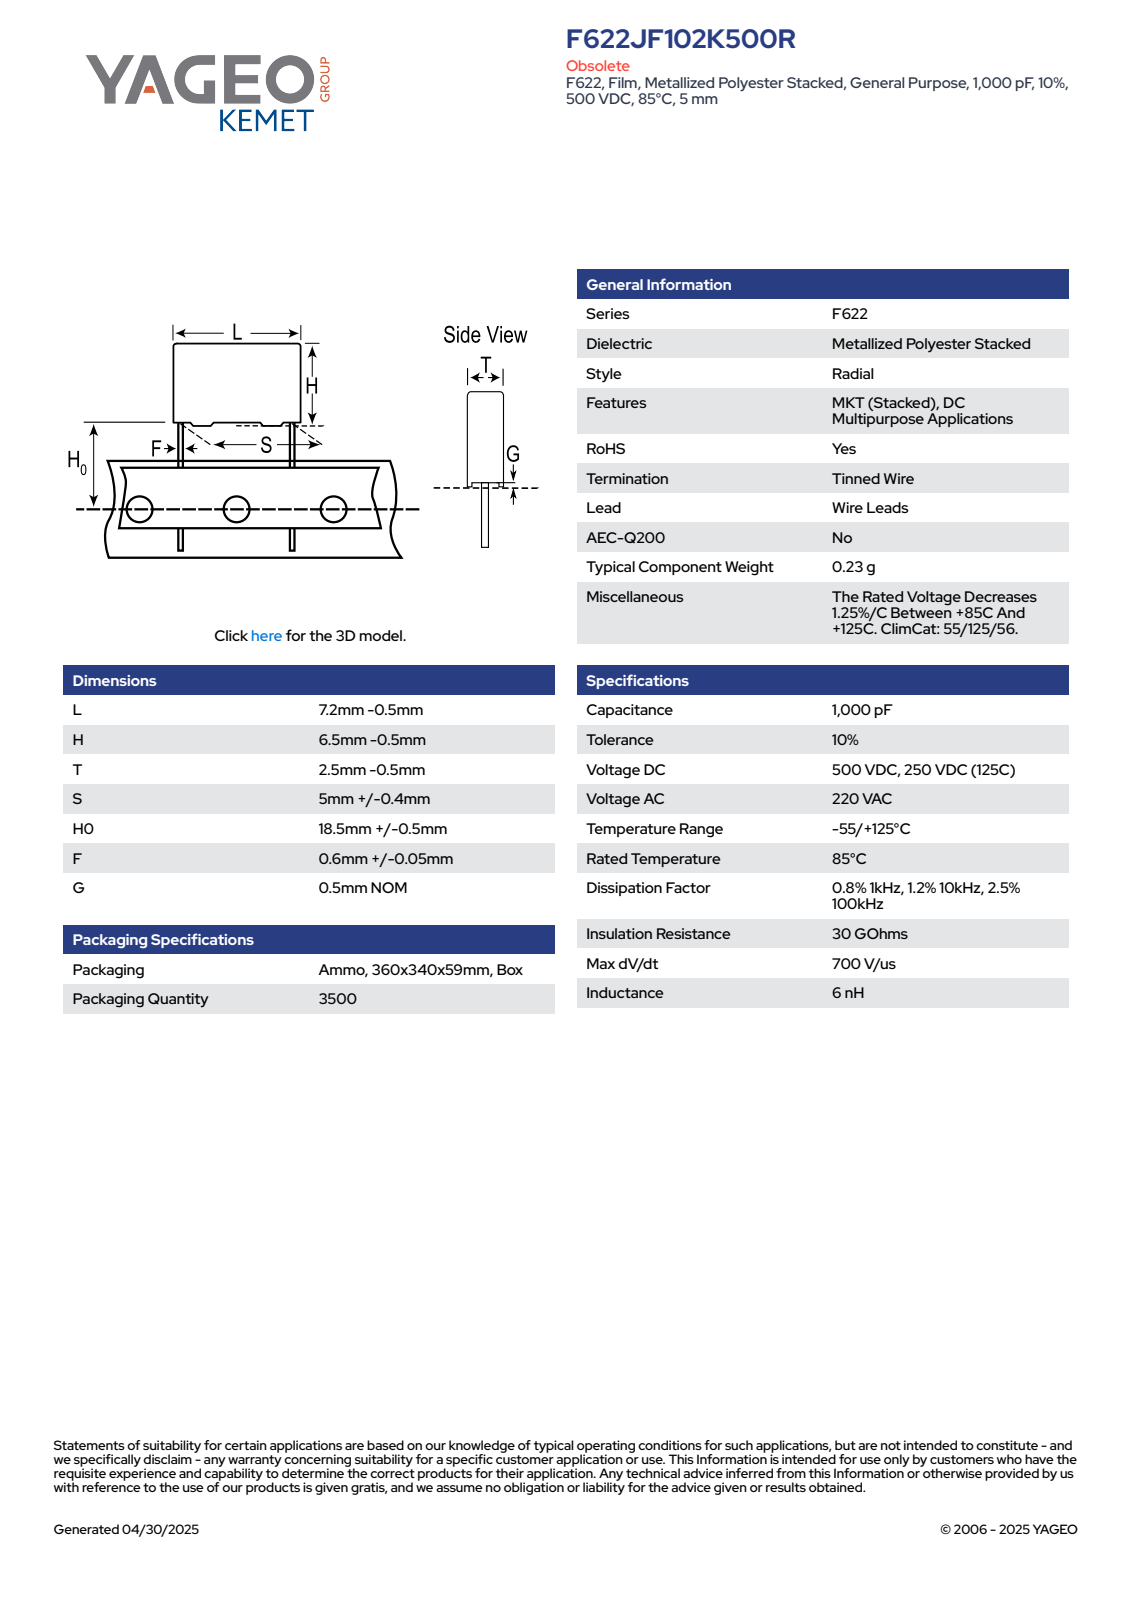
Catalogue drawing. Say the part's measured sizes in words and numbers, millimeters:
The part is named "CFR_RBG_7.2X6.5X2.5_L6.7H6T2S5H019F0.65G0.5". Its 3-D file was written by "SolidWorks 2014 (AUTOMOTIVE_DESIGN)". It is 4 solids with 89 faces: 81 planar, 8 cylindrical and 0 other. Overall it measures 25 by 6.7 by 2 millimeters. Its volume is 86 cubic millimeters and its surface area 208 square millimeters. Round bosses or shafts: 2 of diameter 0.65. Partial cylindrical surfaces (rounded edges, fillets, slot ends): 4 of radius 0.5. The main face-to-face distances are 2, 6.7, 5.5, 1.89, 1.78, 19.5, 25, 19, 0.5, 6.
